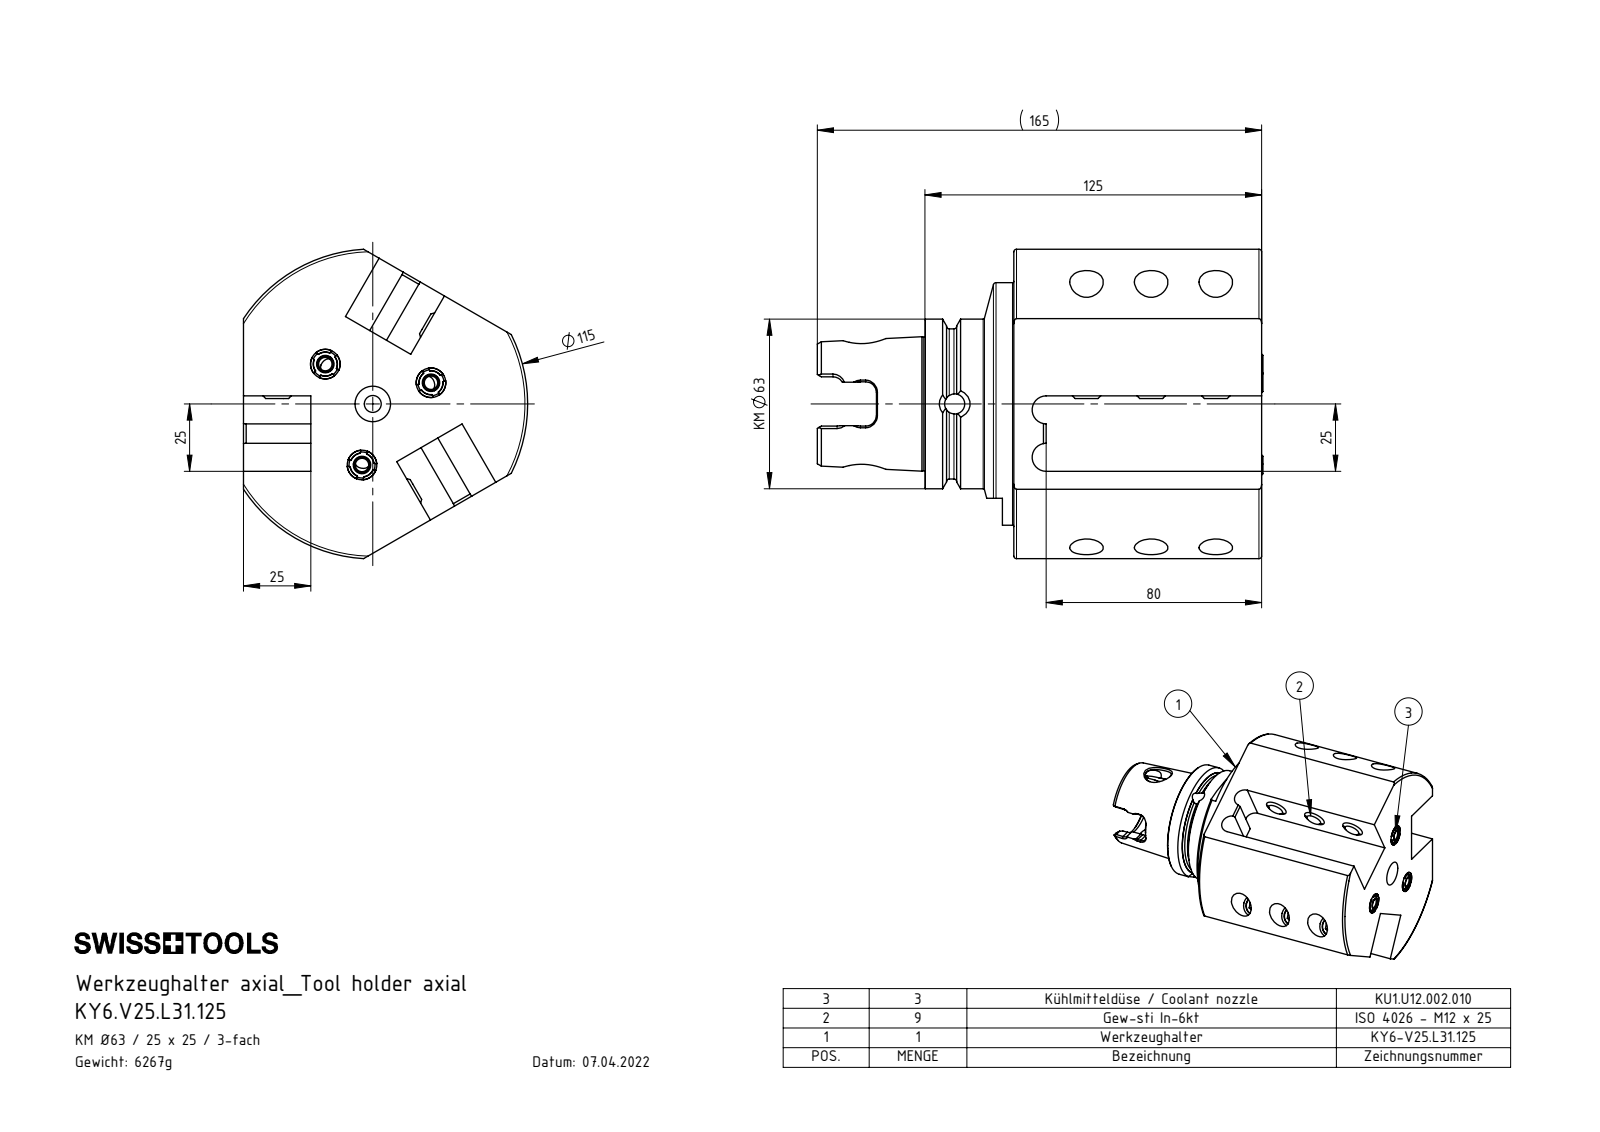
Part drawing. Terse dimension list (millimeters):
name: KU1-U12.003.010_B; KU1-U12.002.010; KY6.V25.L31.125; KU1-U12.002.010_A (+3 more)
written by: SolidWorks 2017 (AUTOMOTIVE_DESIGN)
unit: mm
bodies: 19 solids, 440 faces (188 planar, 95 cylindrical, 157 other)
size: 165.43 × 114.8 × 105.5
volume: 798 243 mm³; area: 110 102 mm²
holes: 9× ⌀10.2, 9× ⌀12.5, 4× ⌀10, 3× ⌀5, 3× ⌀6, 3× ⌀11, 1× ⌀6.3, 1× ⌀7.47, 1× ⌀7.48, 1× ⌀8, 1× ⌀8.48, 1× ⌀11.5
bosses: 12× ⌀12, 1× ⌀90, 1× ⌀62.95, 1× ⌀55.7
rounds: 6× R4, 6× R5.2, 3× R4.4, 2× R7.04, 1× R57.5
face distances: 25, 28, 92, 6, 33, 125, 12, 1.1, 34.1, 126.1
hole spacings: 24, 23, 48, 39.83, 39.84, 89.72, 112.17, 135.15
